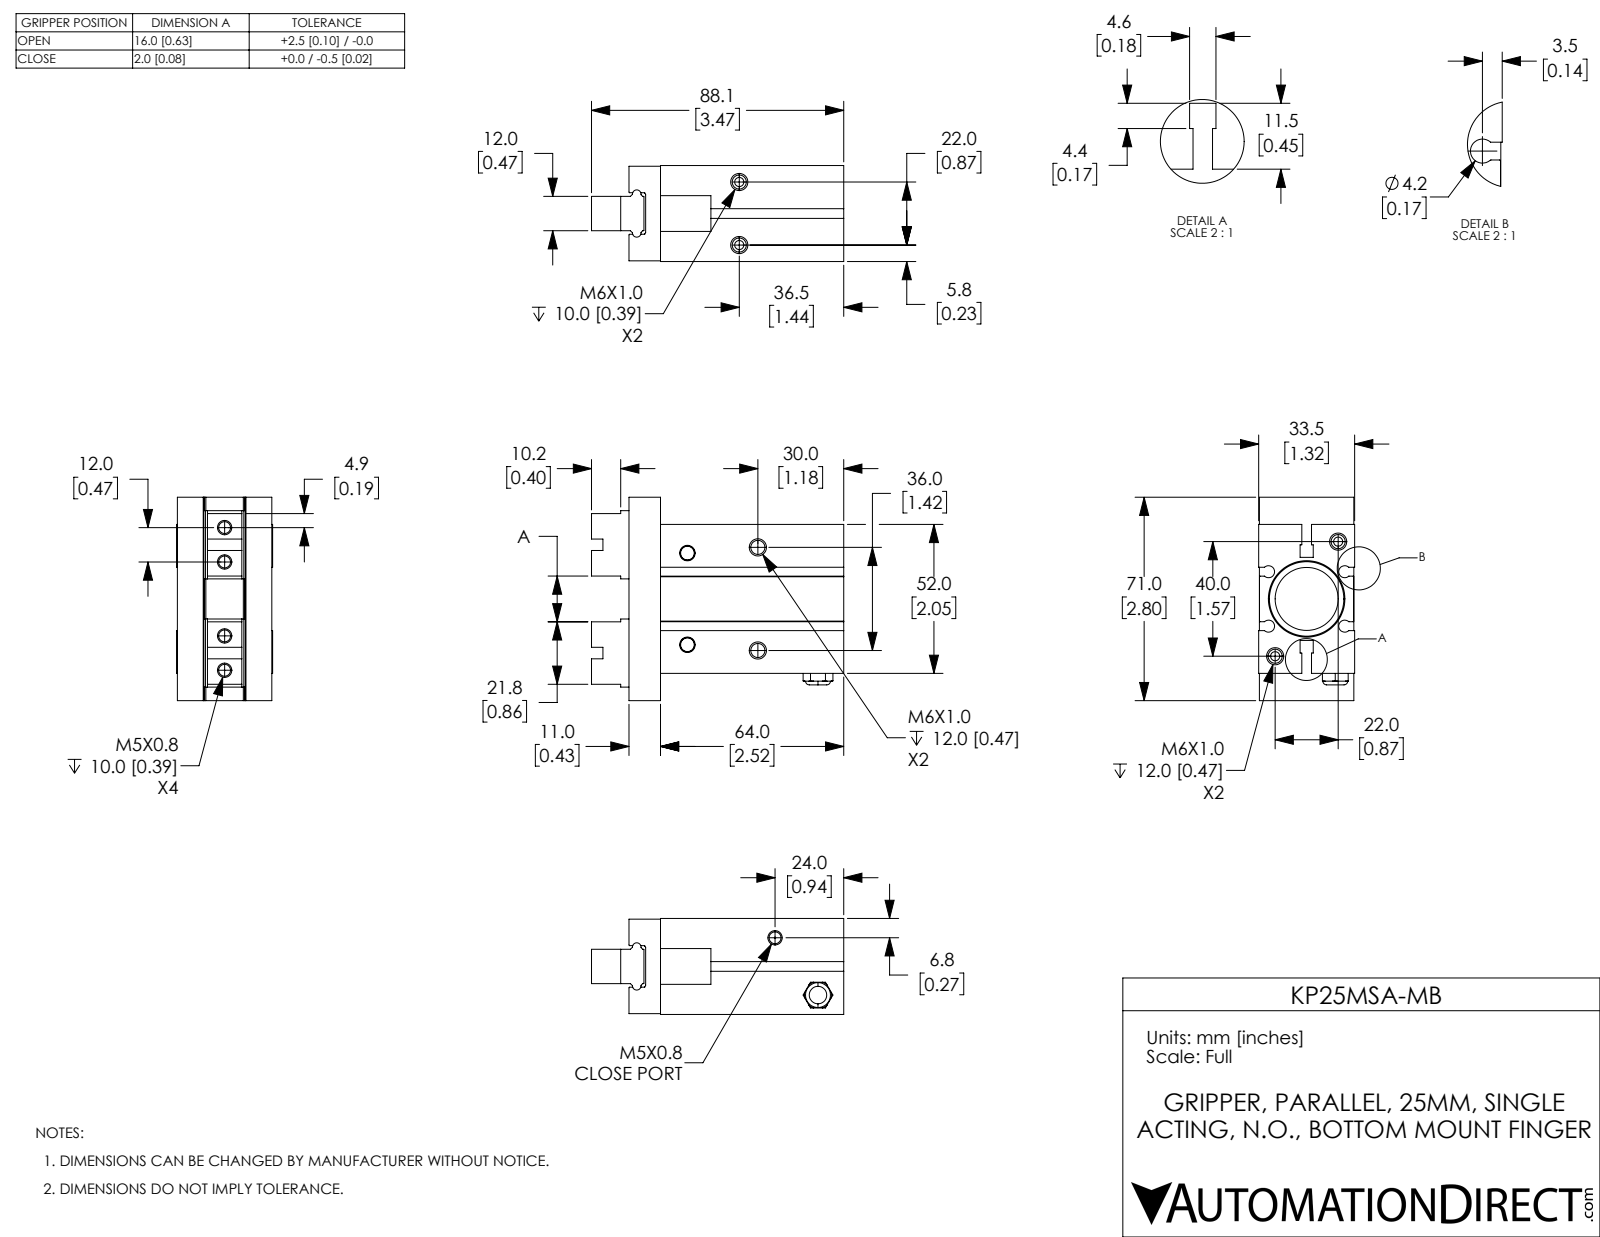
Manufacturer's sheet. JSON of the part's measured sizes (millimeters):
{"part_name": "KP25MSA-MB; KP25MSA-MB-3; KP25MSA-MB-2; KP25MSA-MB-1", "step_written_by": "SolidWorks 2017 (CONFIG_CONTROL_DESIGN)", "units": "millimeters", "bodies": {"solids": 3, "faces": 265, "planar": 137, "cylindrical": 66, "other": 62}, "overall_size": [88.1, 71, 33.5], "volume_mm3": 115913, "surface_area_mm2": 32846, "round_holes": [[4.13, 6], [4.92, 4], [0.5, 2], [4.92, 2], [6.02, 2], [6.1, 1], [22, 1], [26, 1]], "partial_cylinders_radius": [[0.2, 8], [2.1, 4], [0.5, 2], [1.5, 2]], "face_to_face_distances": [10.5, 22.75, 33.2, 10.2, 23, 22.7, 33.5, 52, 33.25, 10.25], "hole_center_spacings": [12, 12.04, 12.9, 13.09, 22.83, 24.9, 34.69, 37.8]}
